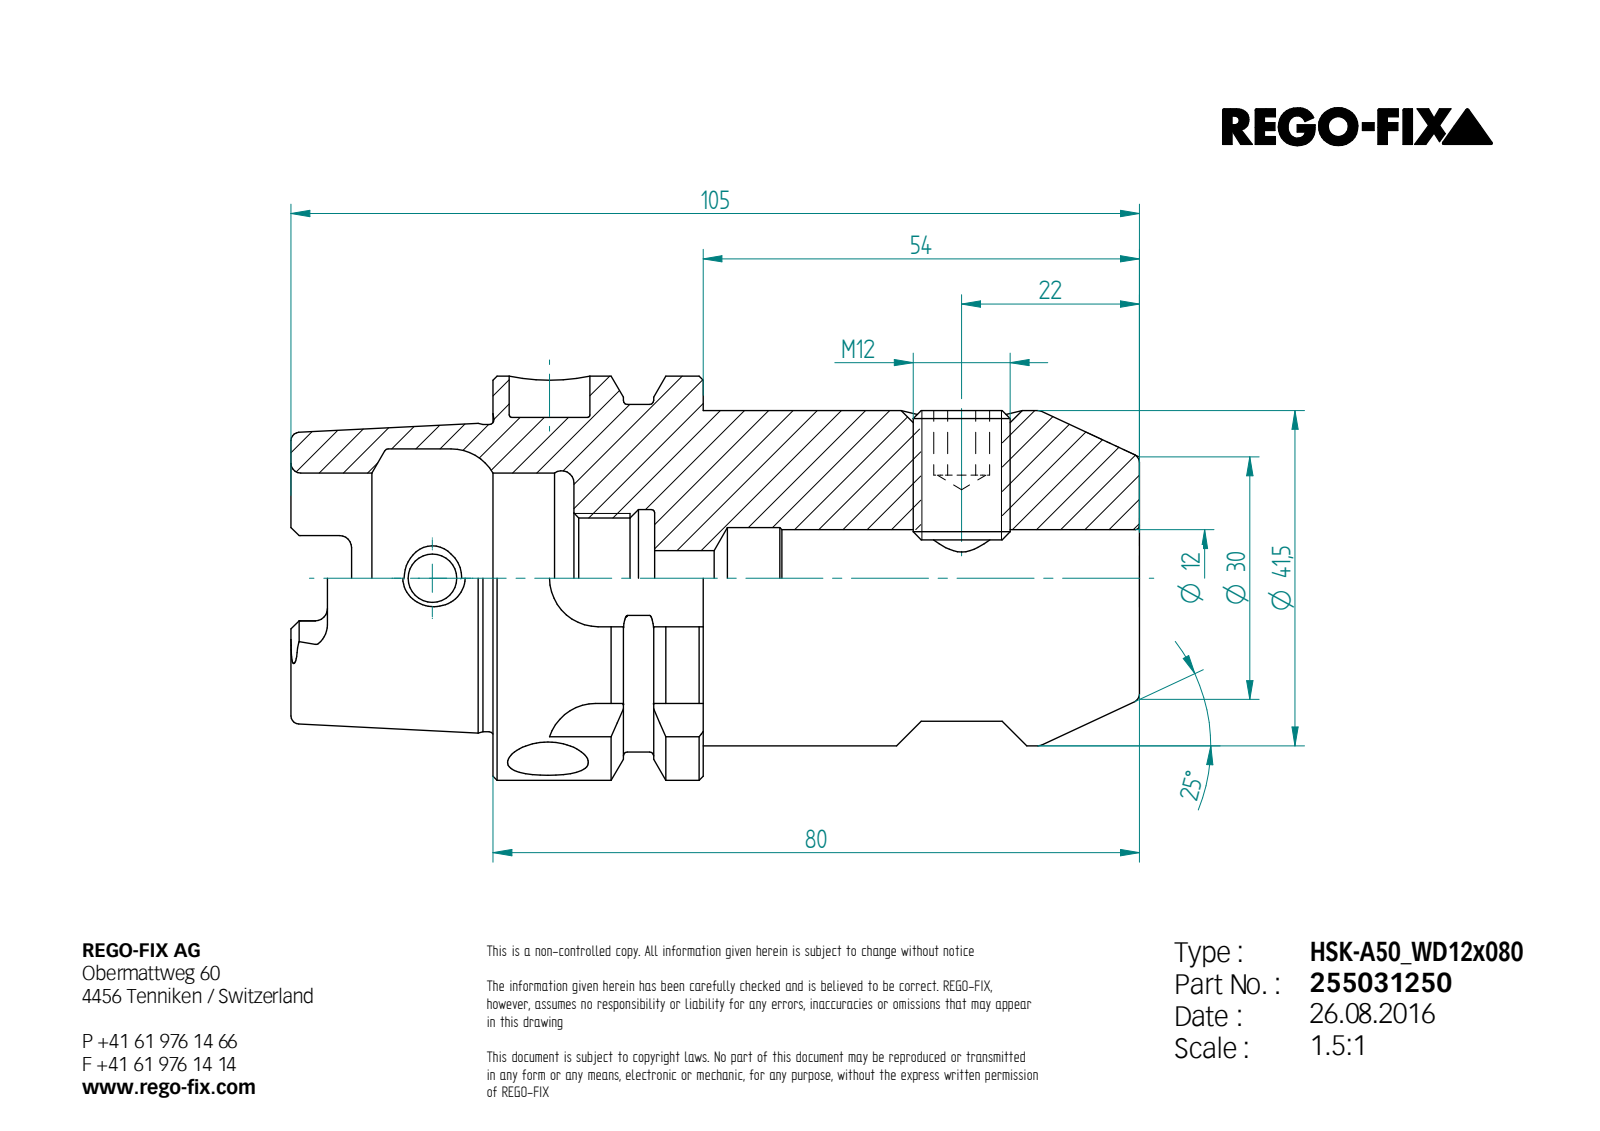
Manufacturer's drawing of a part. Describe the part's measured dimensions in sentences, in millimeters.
Its 3-D file was written by "Unknown (AUTOMOTIVE_DESIGN)". It is 2 solids with 152 faces: 63 planar, 36 cylindrical and 53 other. Overall it measures 105 by 50 by 50 millimeters. Its volume is 111 012 cubic millimeters and its surface area 24 742 square millimeters. Round holes: 2 of diameter 10, 1 of diameter 6, 1 of diameter 6.8, 1 of diameter 10.11, 1 of diameter 12, 1 of diameter 12.5, 1 of diameter 14.92, 1 of diameter 17, 1 of diameter 26, 1 of diameter 32. Round bosses or shafts: 1 of diameter 50, 1 of diameter 43, 1 of diameter 41.5, 1 of diameter 38.01, 1 of diameter 12. Partial cylindrical surfaces (rounded edges, fillets, slot ends): 6 of radius 1.5, 4 of radius 2.38, 4 of radius 6. The main face-to-face distances are 80, 26, 54, 10, 16, 6, 70, 42, 25, 35. The hole center spacings are 51.
